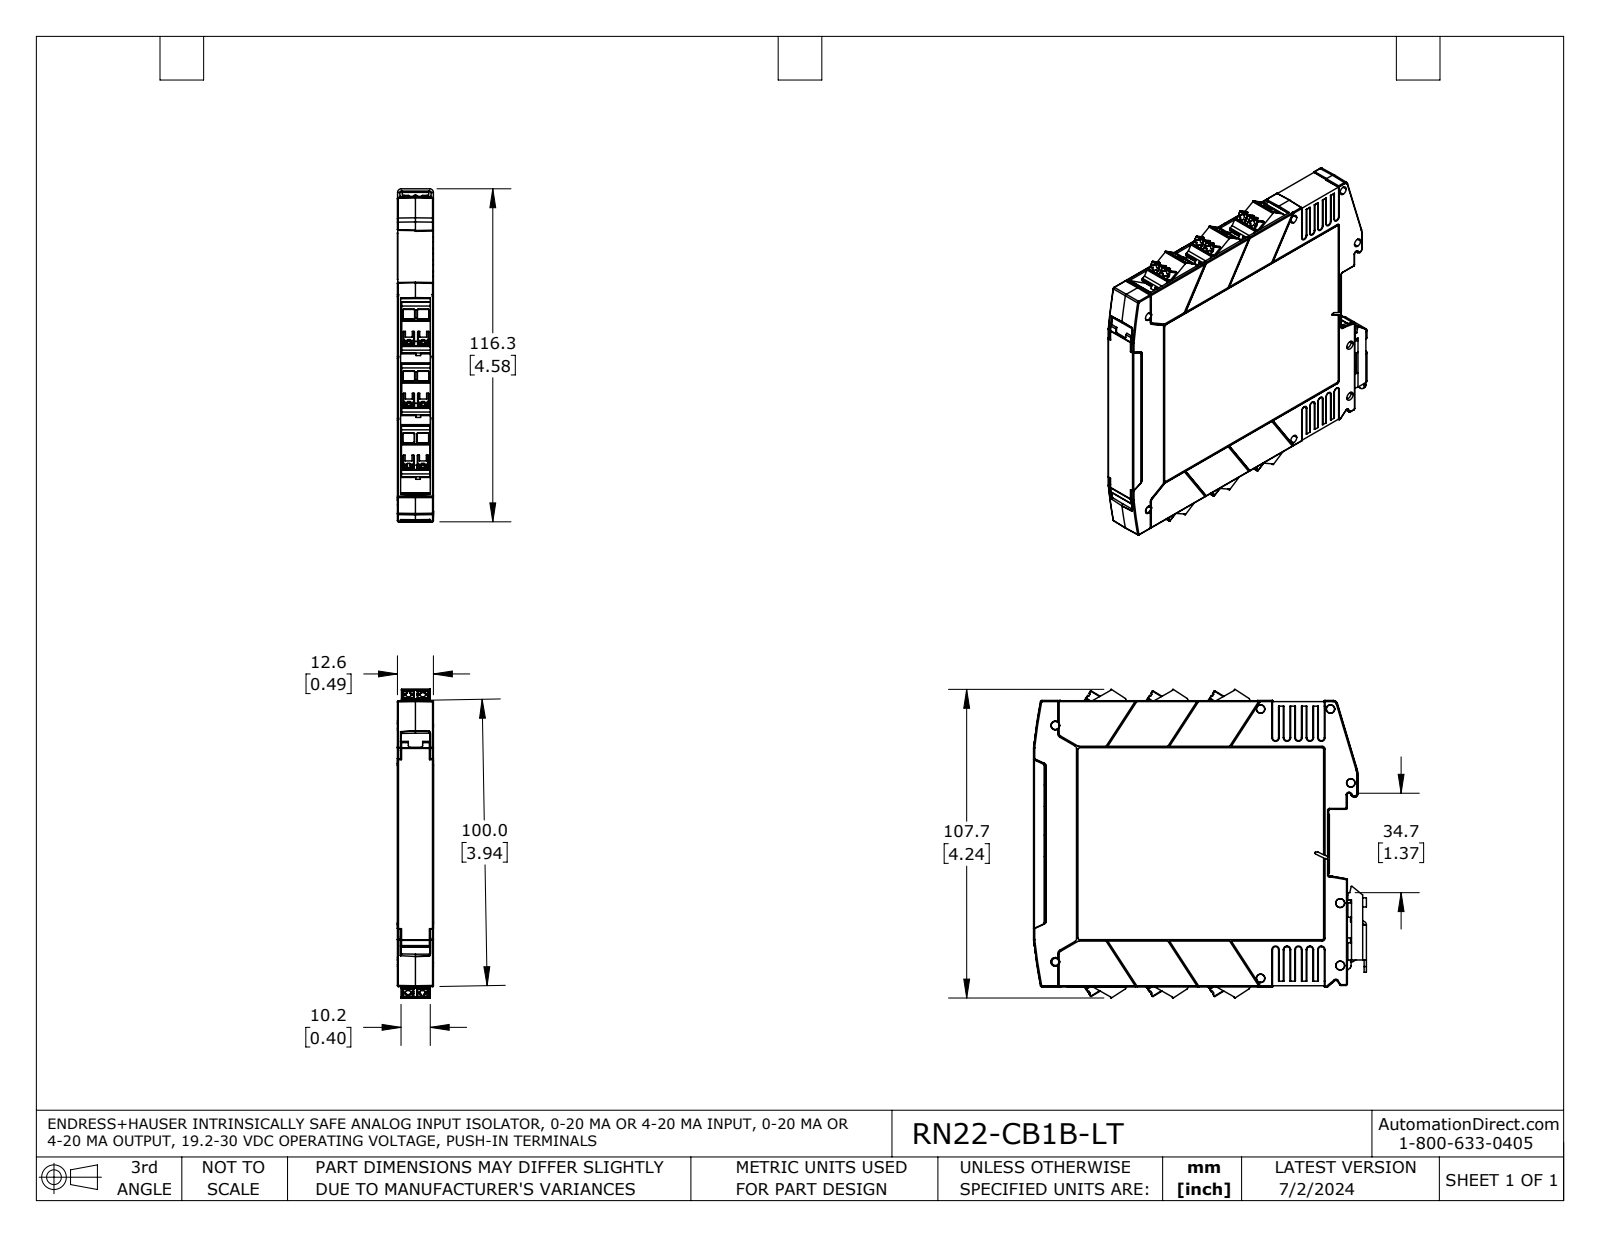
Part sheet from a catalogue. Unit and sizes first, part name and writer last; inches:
Units: inches
Overall size (bounding box): 4.577 × 4.242 × 0.496
Round holes (diameter × count): ⌀0.118 ×3, ⌀0.009 ×2, ⌀0.097 ×1, ⌀0.111 ×1
Partial cylindrical surfaces — rounded edges, fillets, slot ends (radius × count): R0.008 ×149, R0.02 ×71, R0.012 ×66, R0.039 ×28, R0.005 ×16, R0.114 ×12, R0.009 ×10, R0.024 ×10
Main face-to-face distances: 0.494, 0.043, 0.451, 0.039, 0.447, 0.047, 0.491, 0.435, 0.392, 0.031
Hole centre spacings: 2.832, 4.477, 0.759, 0.76, 0.961, 2.073, 2.074, 3.031
Volume: 8.127 in³ · Surface area: 58.24 in²
Bodies: 2 solids, 3045 faces (1939 planar, 765 cylindrical, 341 other)
Part name (STEP PRODUCT): RN22-CB1B-LT
STEP written by: SolidWorks 2021 (AUTOMOTIVE_DESIGN)
